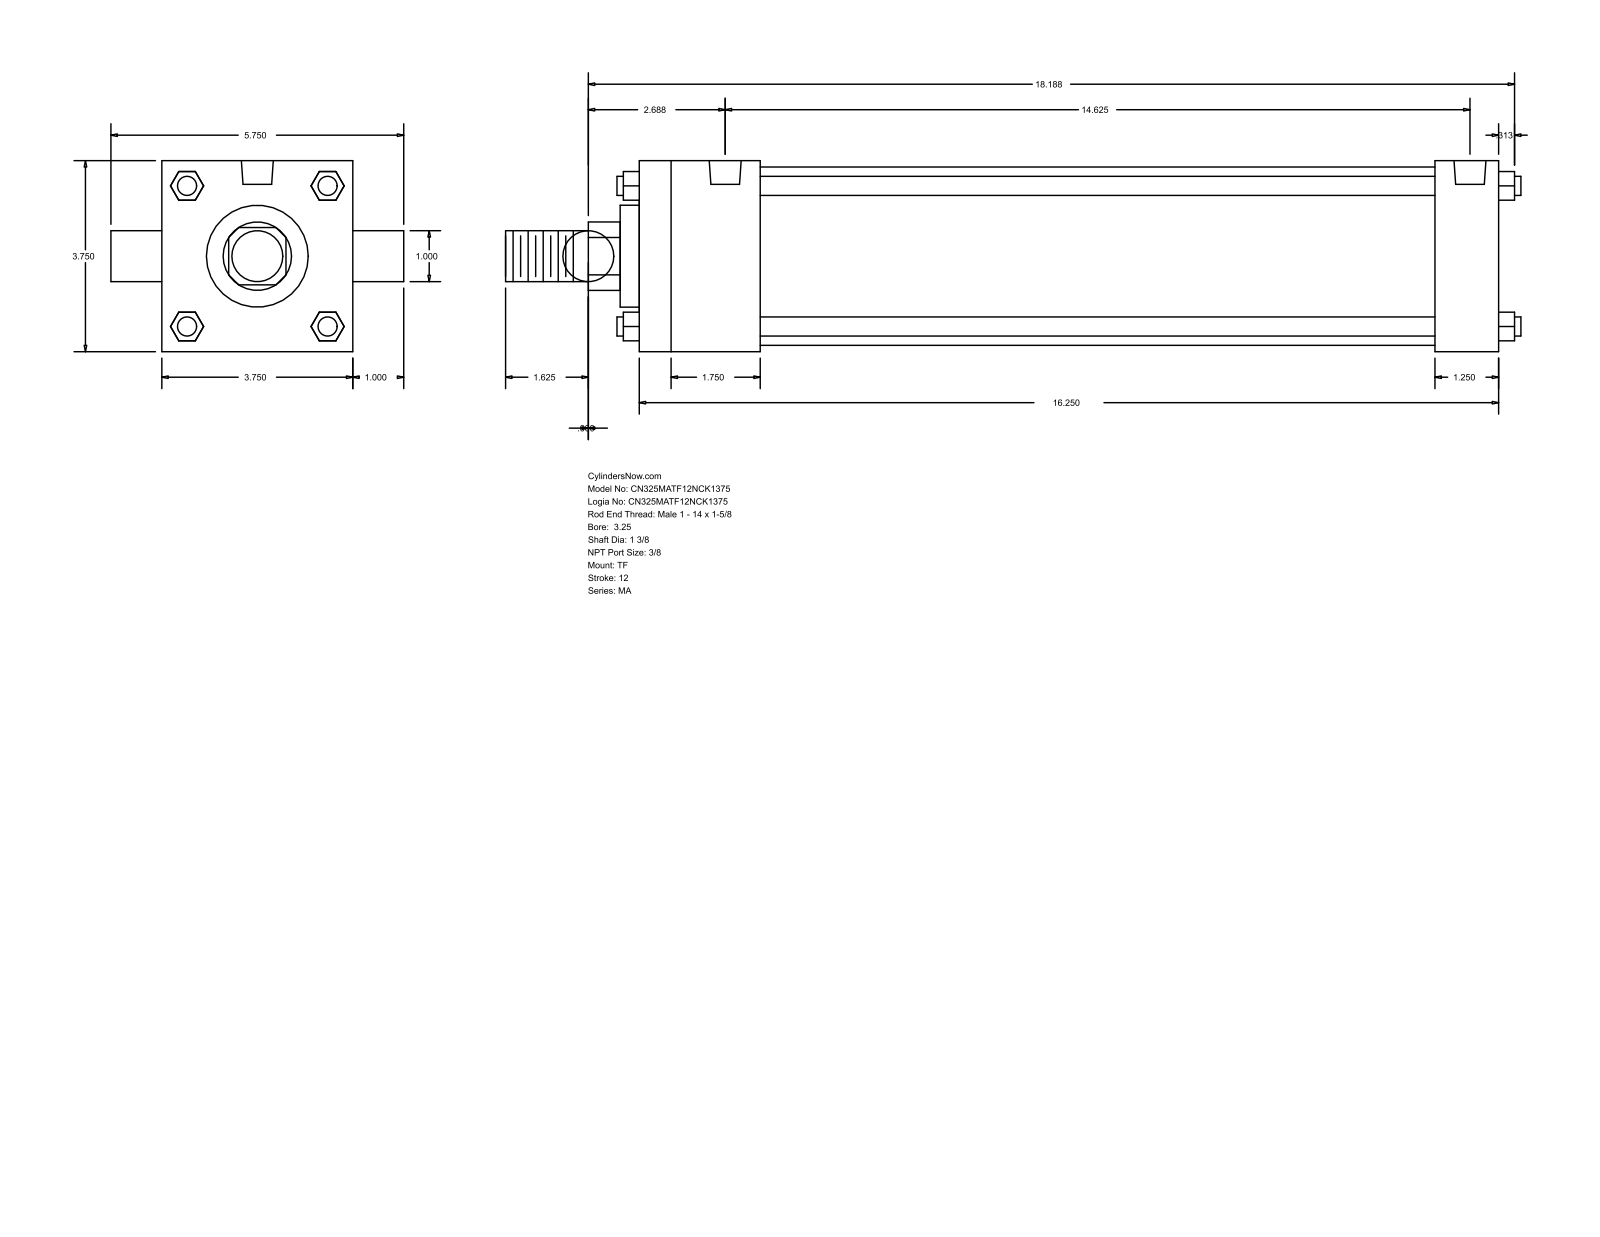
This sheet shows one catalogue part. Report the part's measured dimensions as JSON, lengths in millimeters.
{"part_name": "MA_TF__0325_1.375", "step_written_by": "GSSL Pune (CONFIG_CONTROL_DESIGN)", "units": "millimeters", "bodies": {"solids": 0, "faces": 120, "planar": 92, "cylindrical": 28, "other": 0}, "overall_size": [506.41, 146.05, 95.25], "round_holes": [[11.11, 3], [15.93, 2]], "round_bosses_or_shafts": [[9.53, 4], [25.4, 2], [88.9, 1], [50.8, 1], [34.92, 1]], "partial_cylinders_radius": [[17.06, 1]], "face_to_face_distances": [95.24, 428.62, 60.32, 396.87, 336.55, 368.3, 31.75, 9.52, 69.84, 406.39], "hole_center_spacings": [4.76, 4.77, 361.95, 366.71, 366.72, 371.48]}
